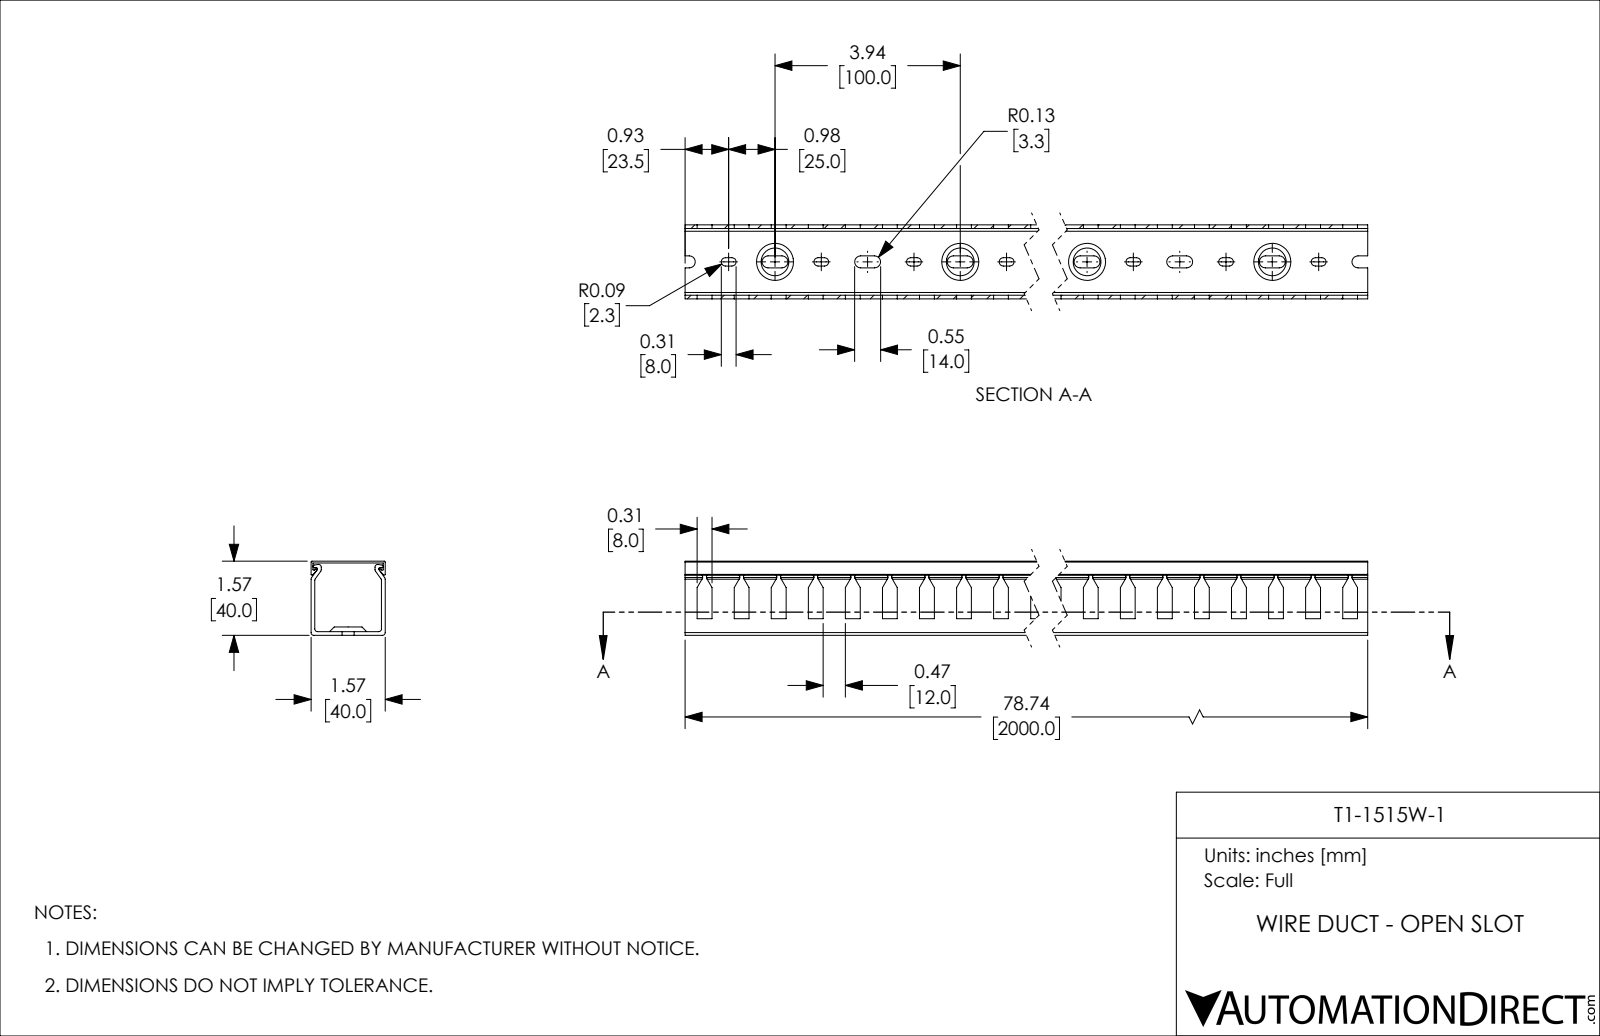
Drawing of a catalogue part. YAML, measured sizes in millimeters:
part_name: "T1-1515W-1"
step_written_by: "SolidWorks 2021 (CONFIG_CONTROL_DESIGN)"
units: millimeters
bodies: {solids: 2, faces: 1005, planar: 534, cylindrical: 431, other: 40}
overall_size: [2000, 40, 40]
volume: 581112
surface_area: 696182
partial_cylinders:
  - {radius: 2.25, count: 80}
  - {radius: 3.25, count: 80}
  - {radius: 1.5, count: 12}
  - {radius: 0.5, count: 8}
  - {radius: 0.75, count: 6}
face_to_face_distances: [2, 38, 40, 1, 39, 37, 36, 4.5, 34.5, 5.5]
